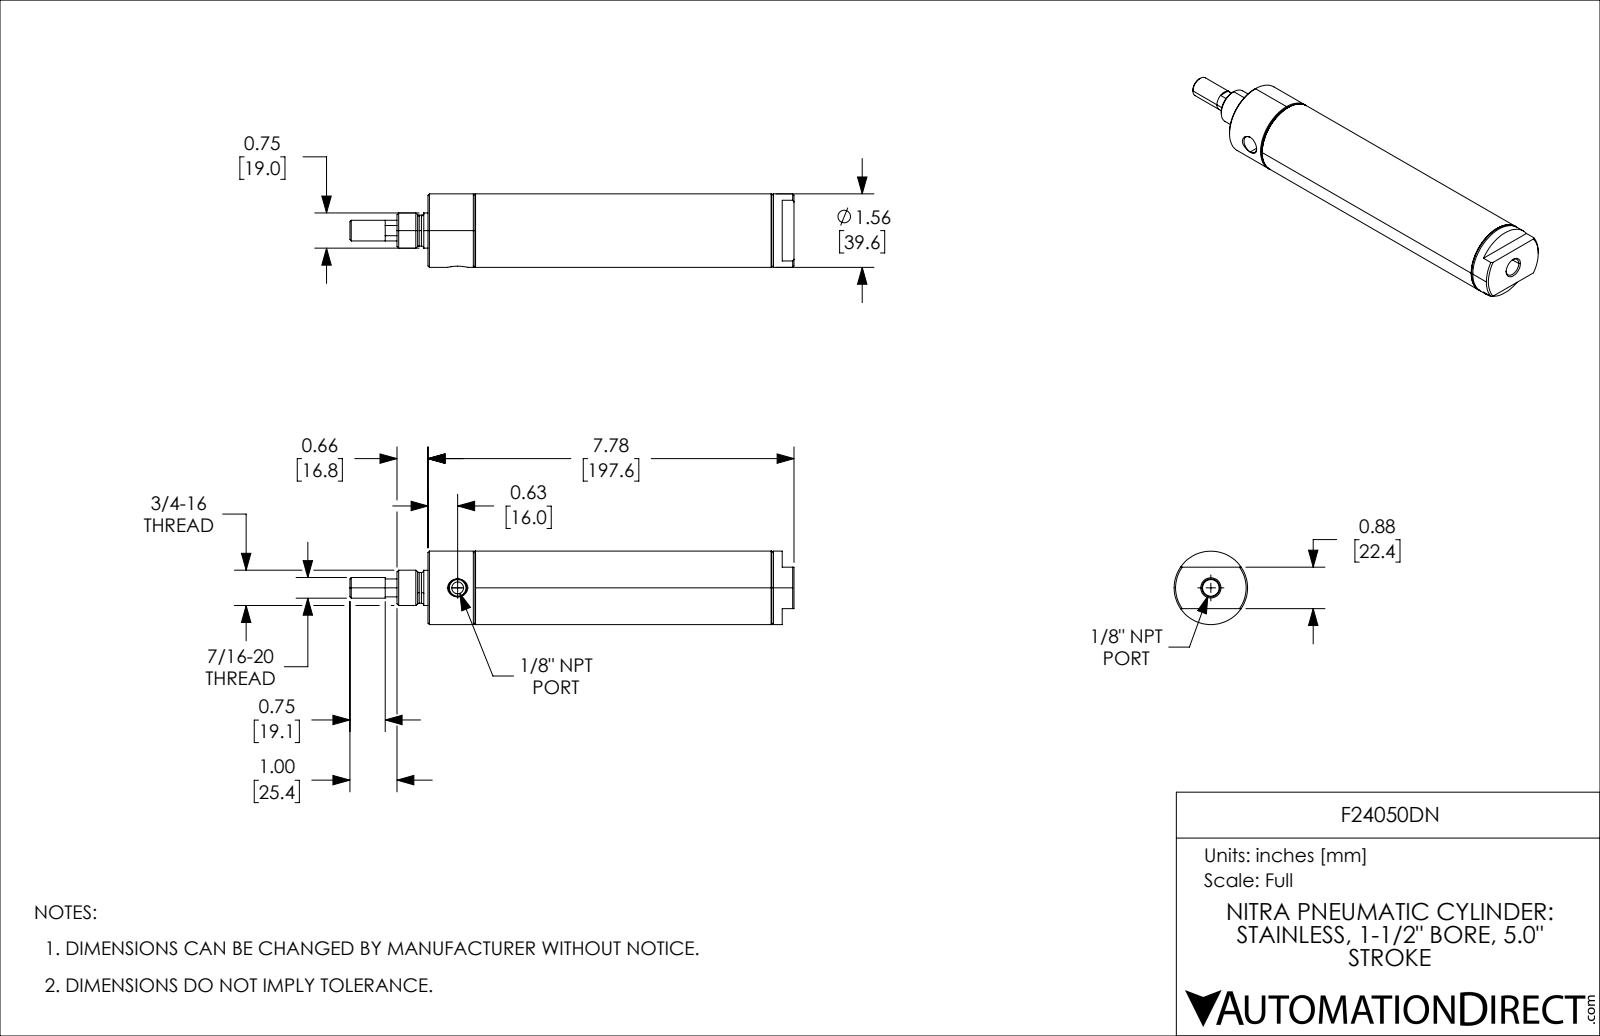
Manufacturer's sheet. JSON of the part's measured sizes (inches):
{"part_name": "F24050DN_3; F24050DN; F24050DN_9; F24050DN_5 (+1 more)", "step_written_by": "SolidWorks 2021 (CONFIG_CONTROL_DESIGN)", "units": "inches", "bodies": {"solids": 4, "faces": 126, "planar": 28, "cylindrical": 42, "other": 56}, "overall_size": [9.438, 1.56, 1.56], "volume_in3": 6.586, "surface_area_in2": 103.9, "round_holes": [[0.25, 1], [0.462, 1], [0.973, 1], [1.431, 1]], "round_bosses_or_shafts": [[1.56, 1], [1.511, 1], [0.75, 1], [0.748, 1], [0.654, 1], [0.438, 1], [0.437, 1]], "face_to_face_distances": [0.875, 0.25, 0.438, 5, 5.875, 1.215, 6.215, 7.09, 7.778, 6.563]}
